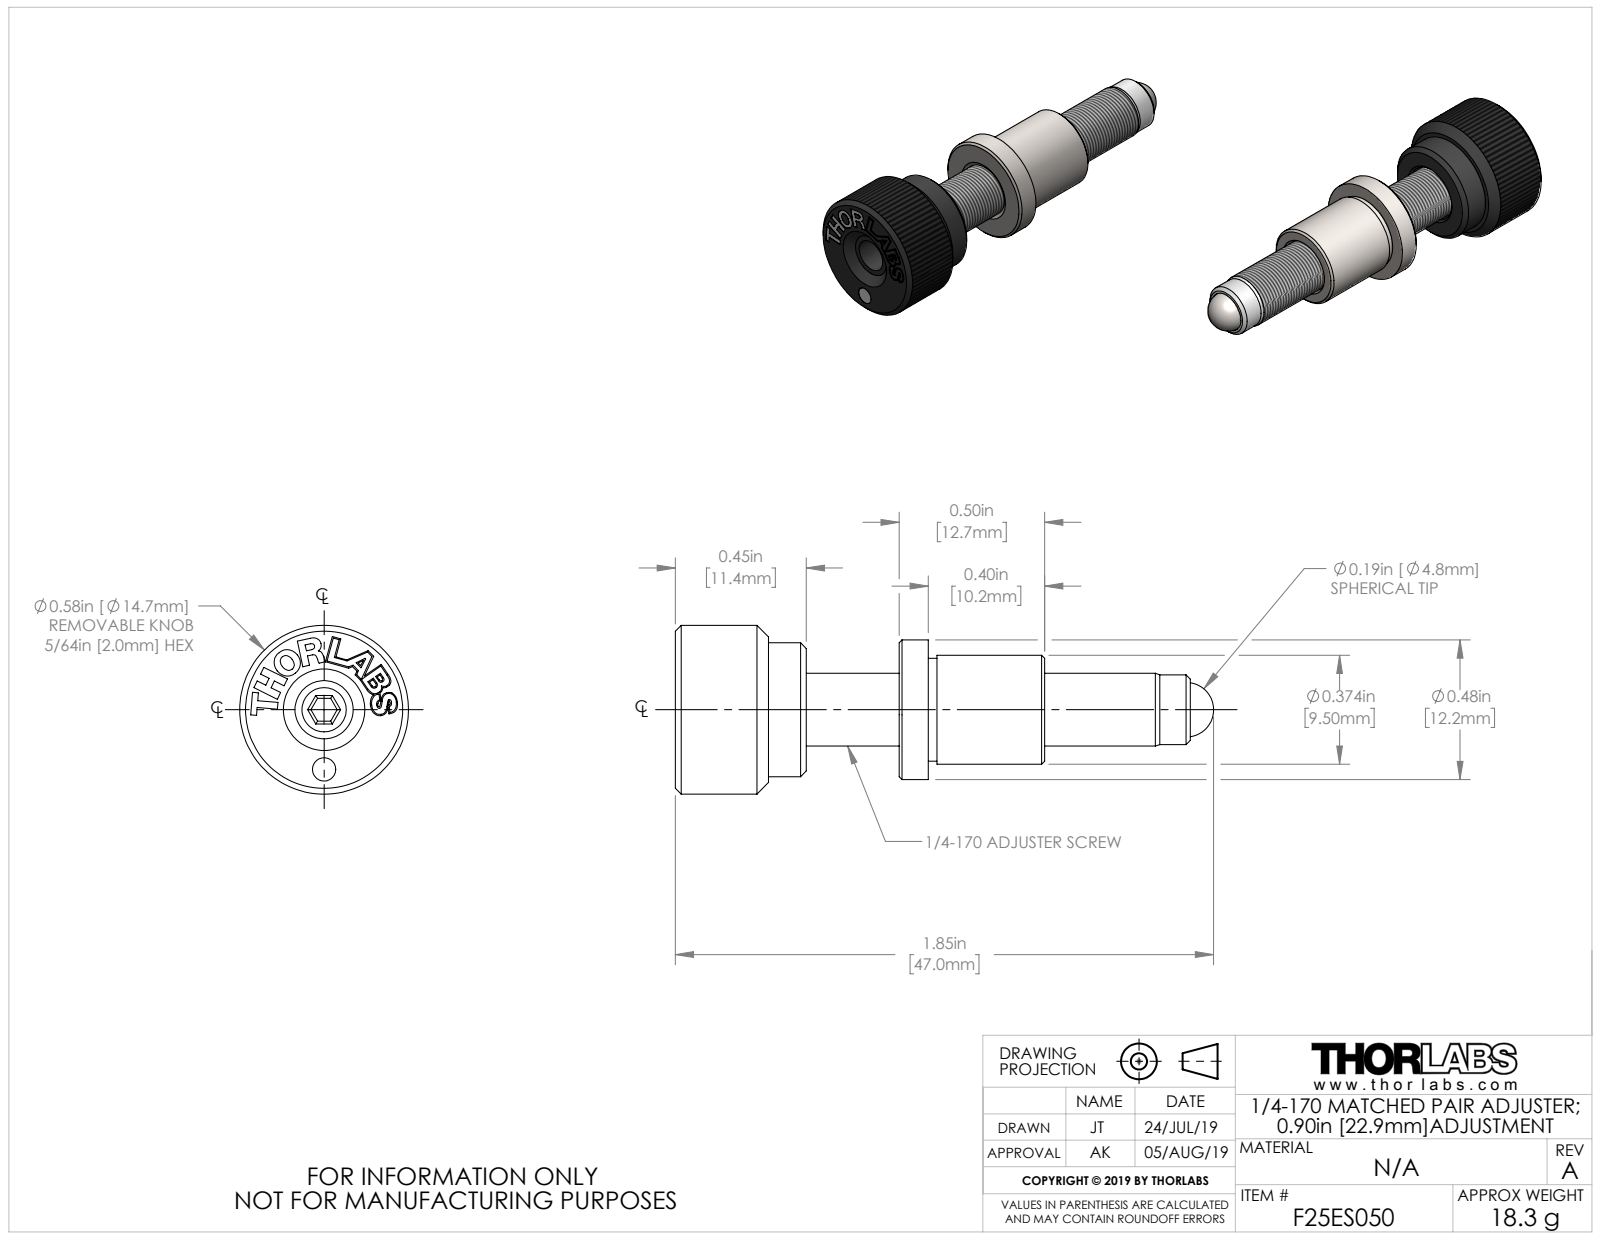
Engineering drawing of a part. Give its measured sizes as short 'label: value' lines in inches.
name: TTN192476-E0W
written by: SolidWorks 2018 (AUTOMOTIVE_DESIGN)
unit: in
bodies: 4 solids, 265 faces (139 planar, 37 cylindrical, 89 other)
size: 1.85 × 0.58 × 0.58
volume: 0.198 in³; area: 4.217 in²
holes: 1× ⌀0.08, 1× ⌀0.152, 1× ⌀0.188, 1× ⌀0.245, 1× ⌀0.265, 1× ⌀0.29
bosses: 1× ⌀0.58, 1× ⌀0.48, 1× ⌀0.46, 1× ⌀0.374, 1× ⌀0.354, 1× ⌀0.25, 1× ⌀0.24, 1× ⌀0.21
rounds: 1× R0.014, 1× R0.047, 1× R0.059
face distances: 0.769, 0.1, 0.499, 0.869, 0.27, 0.599, 0.45, 0.18, 0.319, 0.419
hole spacings: 0.205
